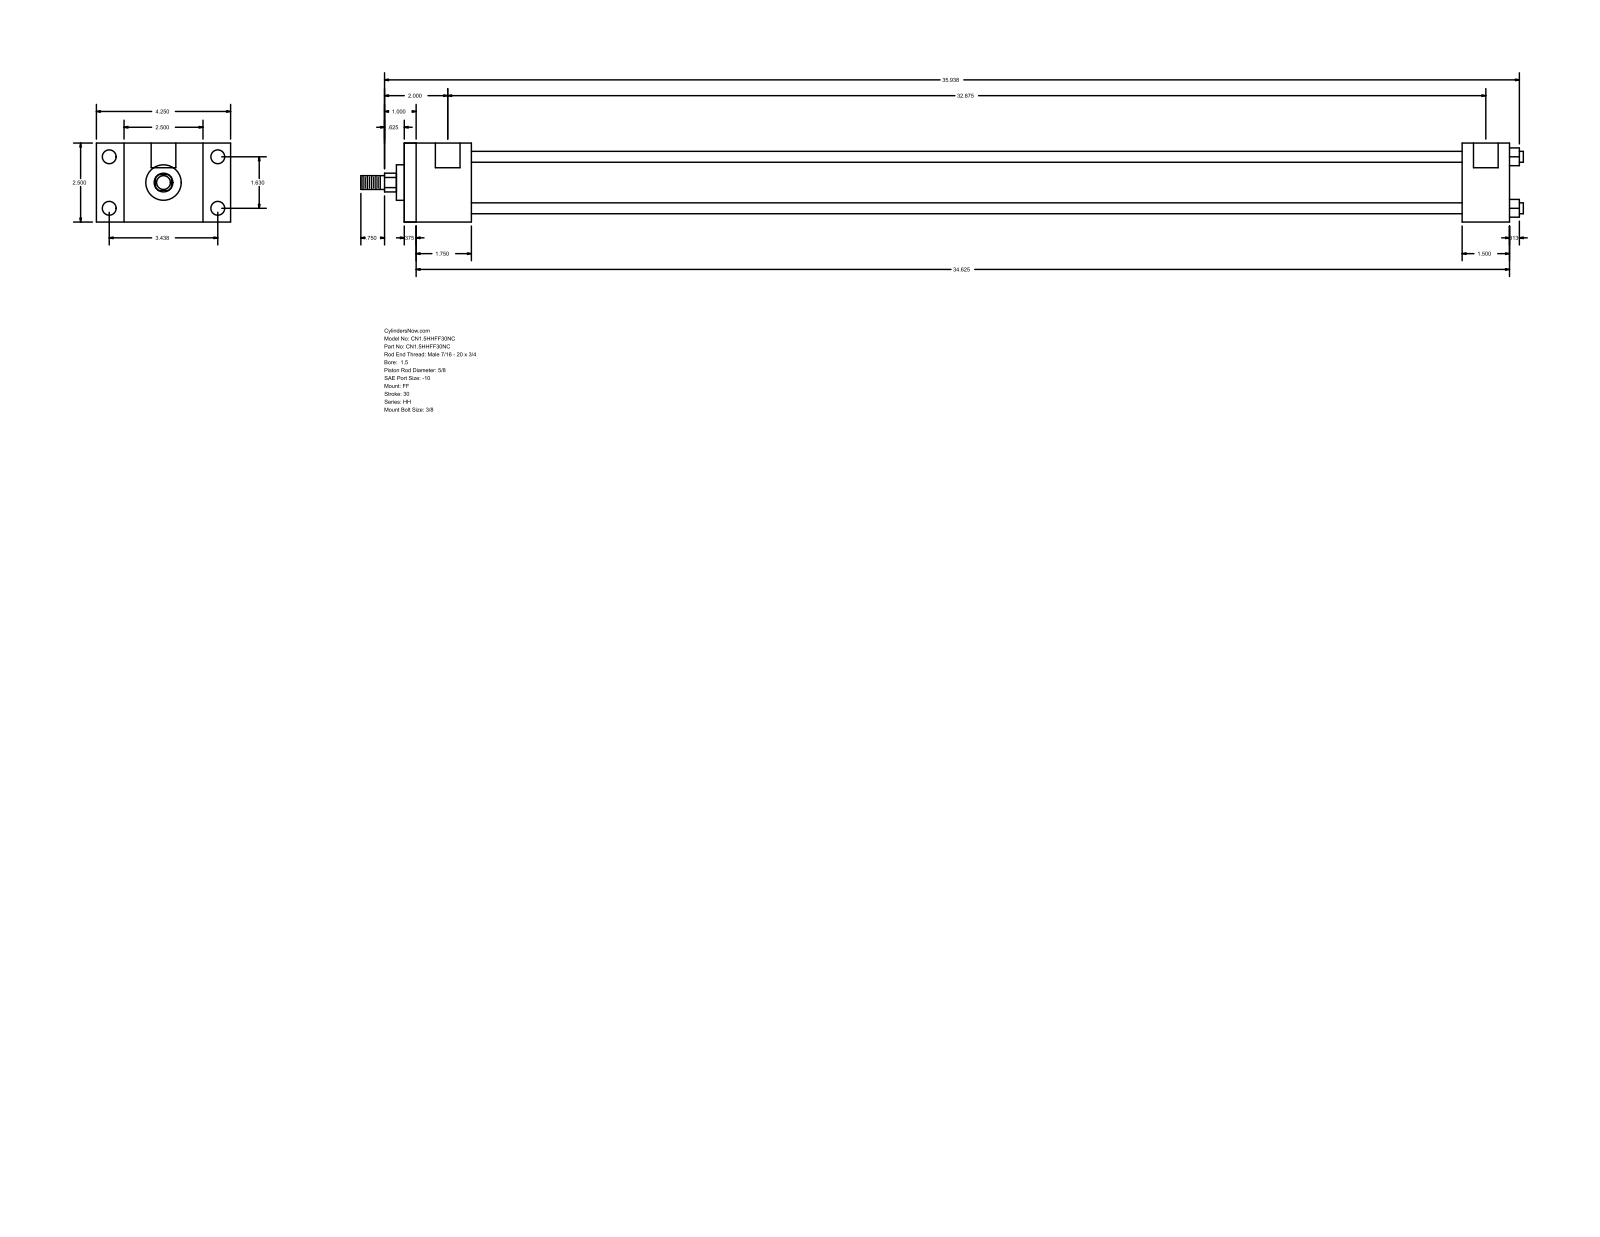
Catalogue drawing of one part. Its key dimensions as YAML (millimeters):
part_name: "HH_FF__0150_0.625"
step_written_by: "GSSL Pune (CONFIG_CONTROL_DESIGN)"
units: millimeters
bodies: {solids: 0, faces: 92, planar: 64, cylindrical: 28, other: 0}
overall_size: [935.04, 107.95, 63.5]
round_holes:
  - {diameter: 5.56, count: 4}
  - {diameter: 11.13, count: 4}
  - {diameter: 19.84, count: 2}
round_bosses_or_shafts:
  - {diameter: 8.76, count: 4}
  - {diameter: 44.45, count: 1}
  - {diameter: 28.57, count: 1}
  - {diameter: 15.88, count: 1}
  - {diameter: 11.11, count: 1}
partial_cylinders:
  - {radius: 7.54, count: 1}
face_to_face_distances: [63.5, 889, 9.52, 879.48, 44.45, 53.97, 835.03, 850.89, 841.37, 796.92]
hole_center_spacings: [41.4, 87.32, 96.64, 838.2, 1.58, 1.59, 835.03, 836.61]
